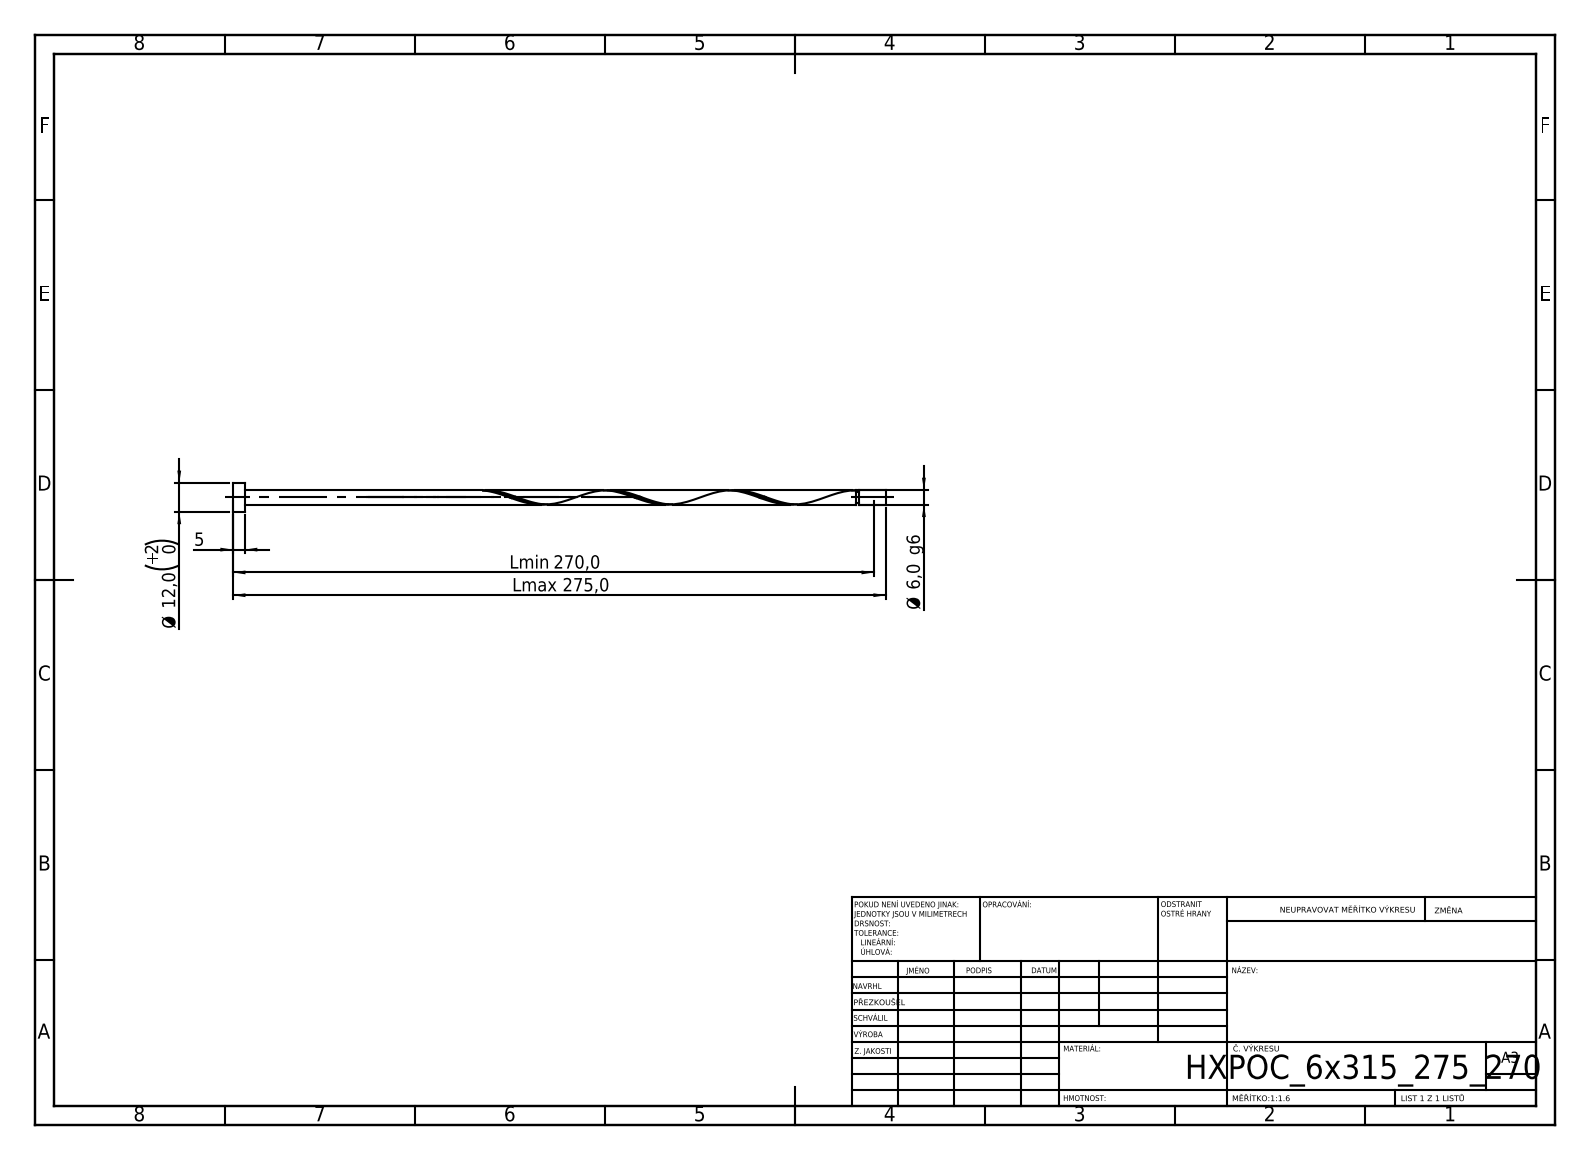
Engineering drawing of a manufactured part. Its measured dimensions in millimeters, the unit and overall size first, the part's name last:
Units: millimetres
Overall size (bounding box): 275 × 12 × 12
Round bosses / shafts (diameter × count): ⌀12 ×1, ⌀6 ×1, ⌀4.8 ×1
Main face-to-face distances: 5, 275, 270, 263.67, 258.67, 11.33, 262.47, 257.47, 1.2, 12.53
Volume: 8 102 mm³ · Surface area: 5 617 mm²
Bodies: 1 solid, 21 faces (6 planar, 14 cylindrical, 1 other)
STEP written by: SolidWorks 2019 (CONFIG_CONTROL_DESIGN)
